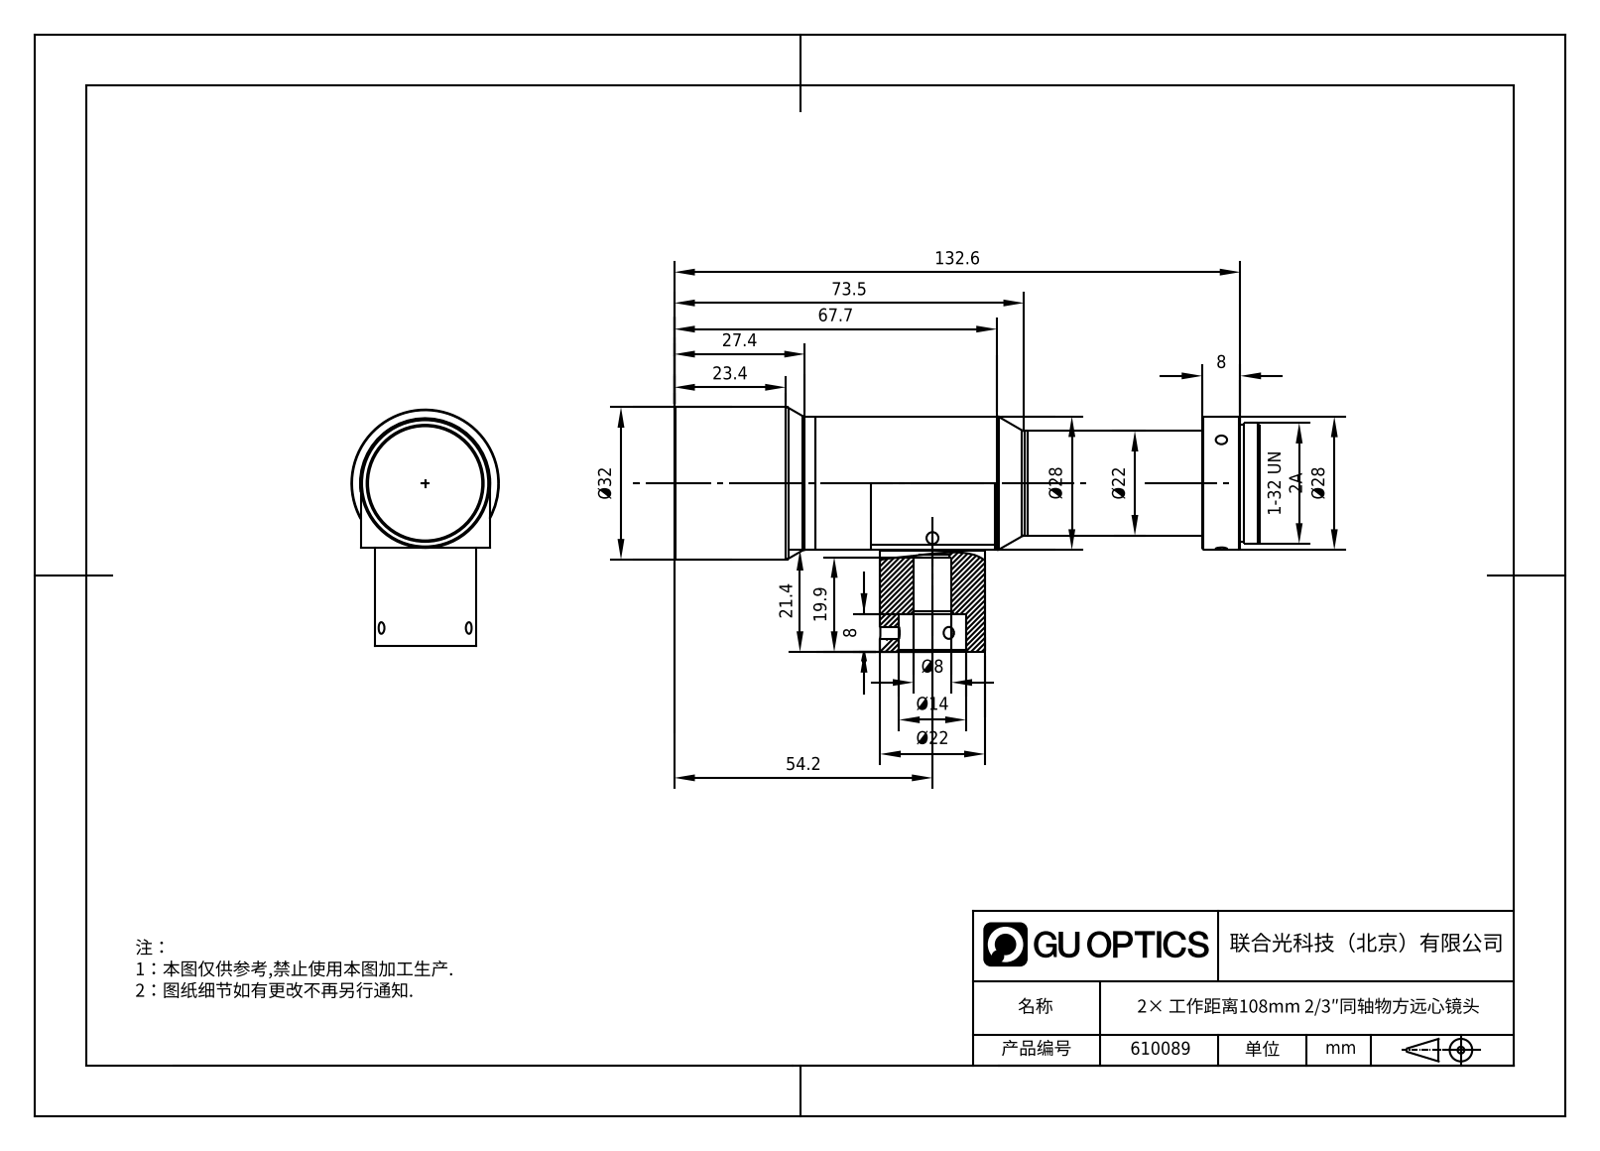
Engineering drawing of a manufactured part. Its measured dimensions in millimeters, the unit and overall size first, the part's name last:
Units: millimetres
Overall size (bounding box): 136.6 × 51.4 × 32
Round holes (diameter × count): ⌀8 ×1, ⌀14 ×1
Round bosses / shafts (diameter × count): ⌀22 ×2, ⌀32 ×1, ⌀28 ×1, ⌀25.4 ×1, ⌀24.4 ×1
Main face-to-face distances: 136.6, 28, 21.4, 8, 124.6, 12, 132.6, 4, 13.4, 41.2
Volume: 84 153 mm³ · Surface area: 15 672 mm²
Bodies: 1 solid, 54 faces (15 planar, 19 cylindrical, 20 other)
Part name (STEP PRODUCT): WWH20-108CTV3
STEP written by: SolidWorks 2017 (CONFIG_CONTROL_DESIGN)
